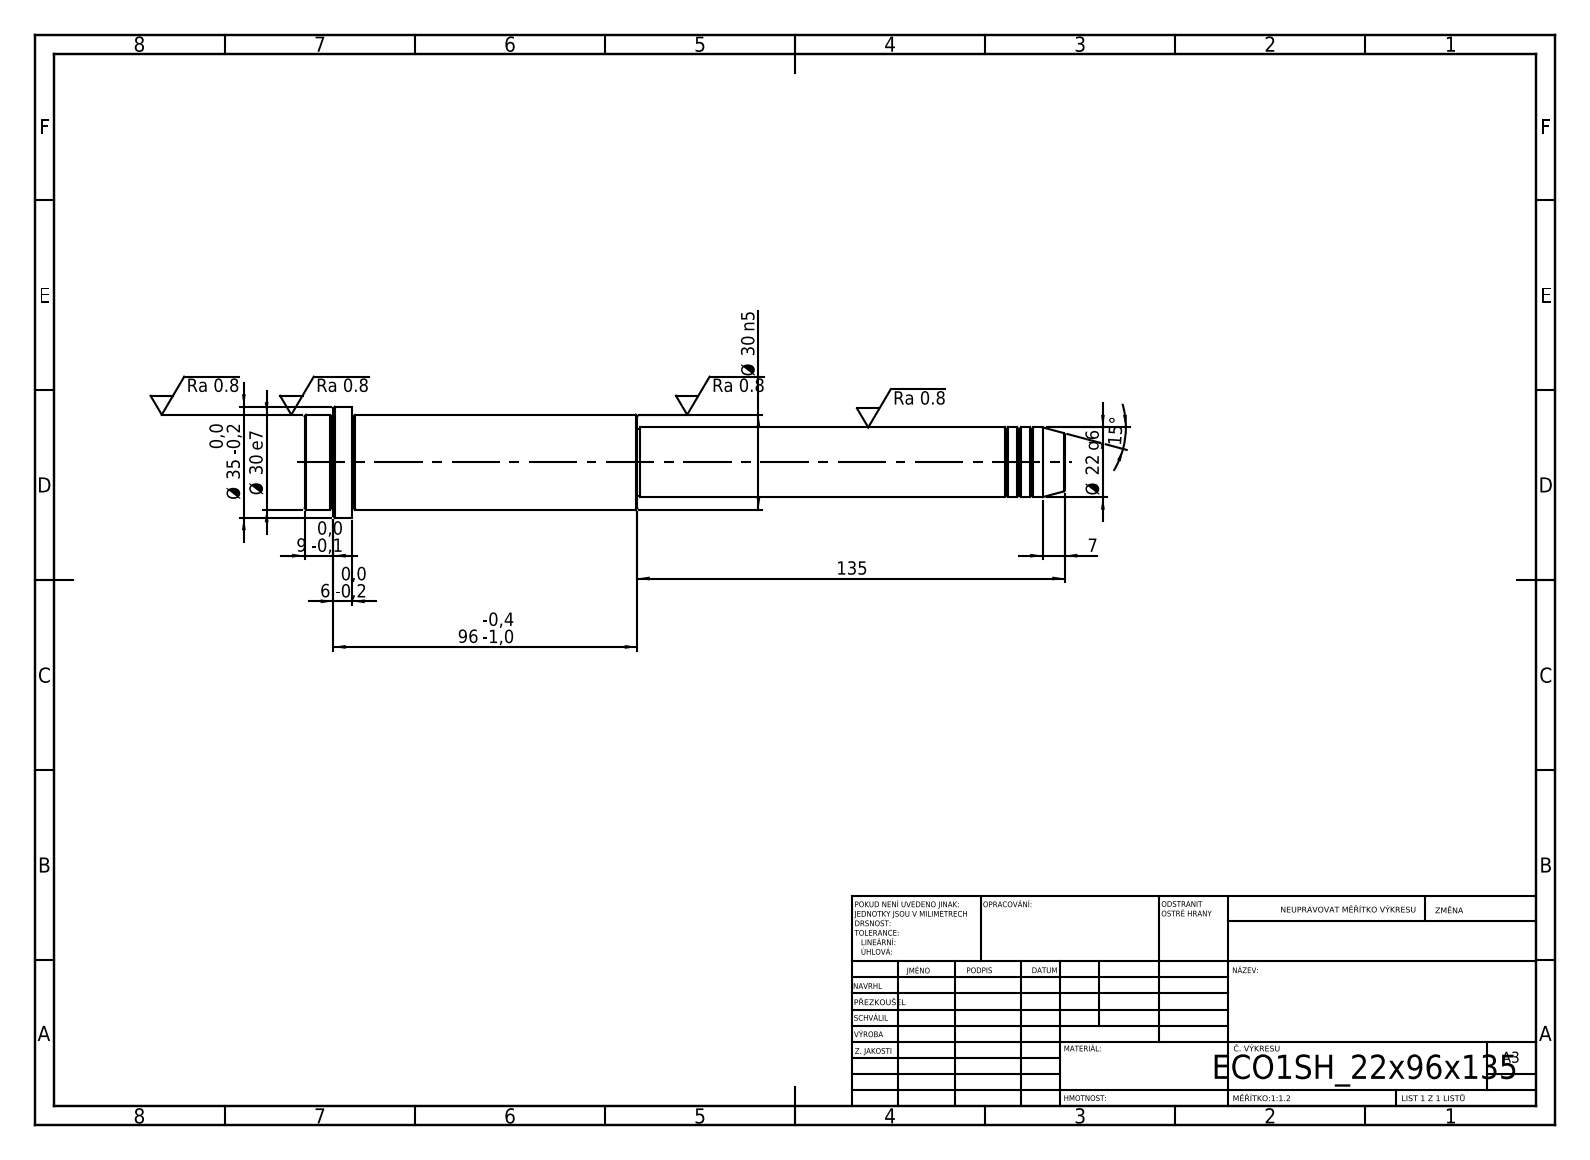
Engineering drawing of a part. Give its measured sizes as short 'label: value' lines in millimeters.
written by: SolidWorks 2019 (CONFIG_CONTROL_DESIGN)
unit: mm
bodies: 1 solid, 52 faces (6 planar, 16 cylindrical, 30 other)
size: 240 × 35 × 35
volume: 126 417 mm³; area: 21 281 mm²
bosses: 1× ⌀35, 1× ⌀30, 1× ⌀22, 1× ⌀21
face distances: 105, 90, 15, 135, 225, 240, 231, 96, 6, 9
